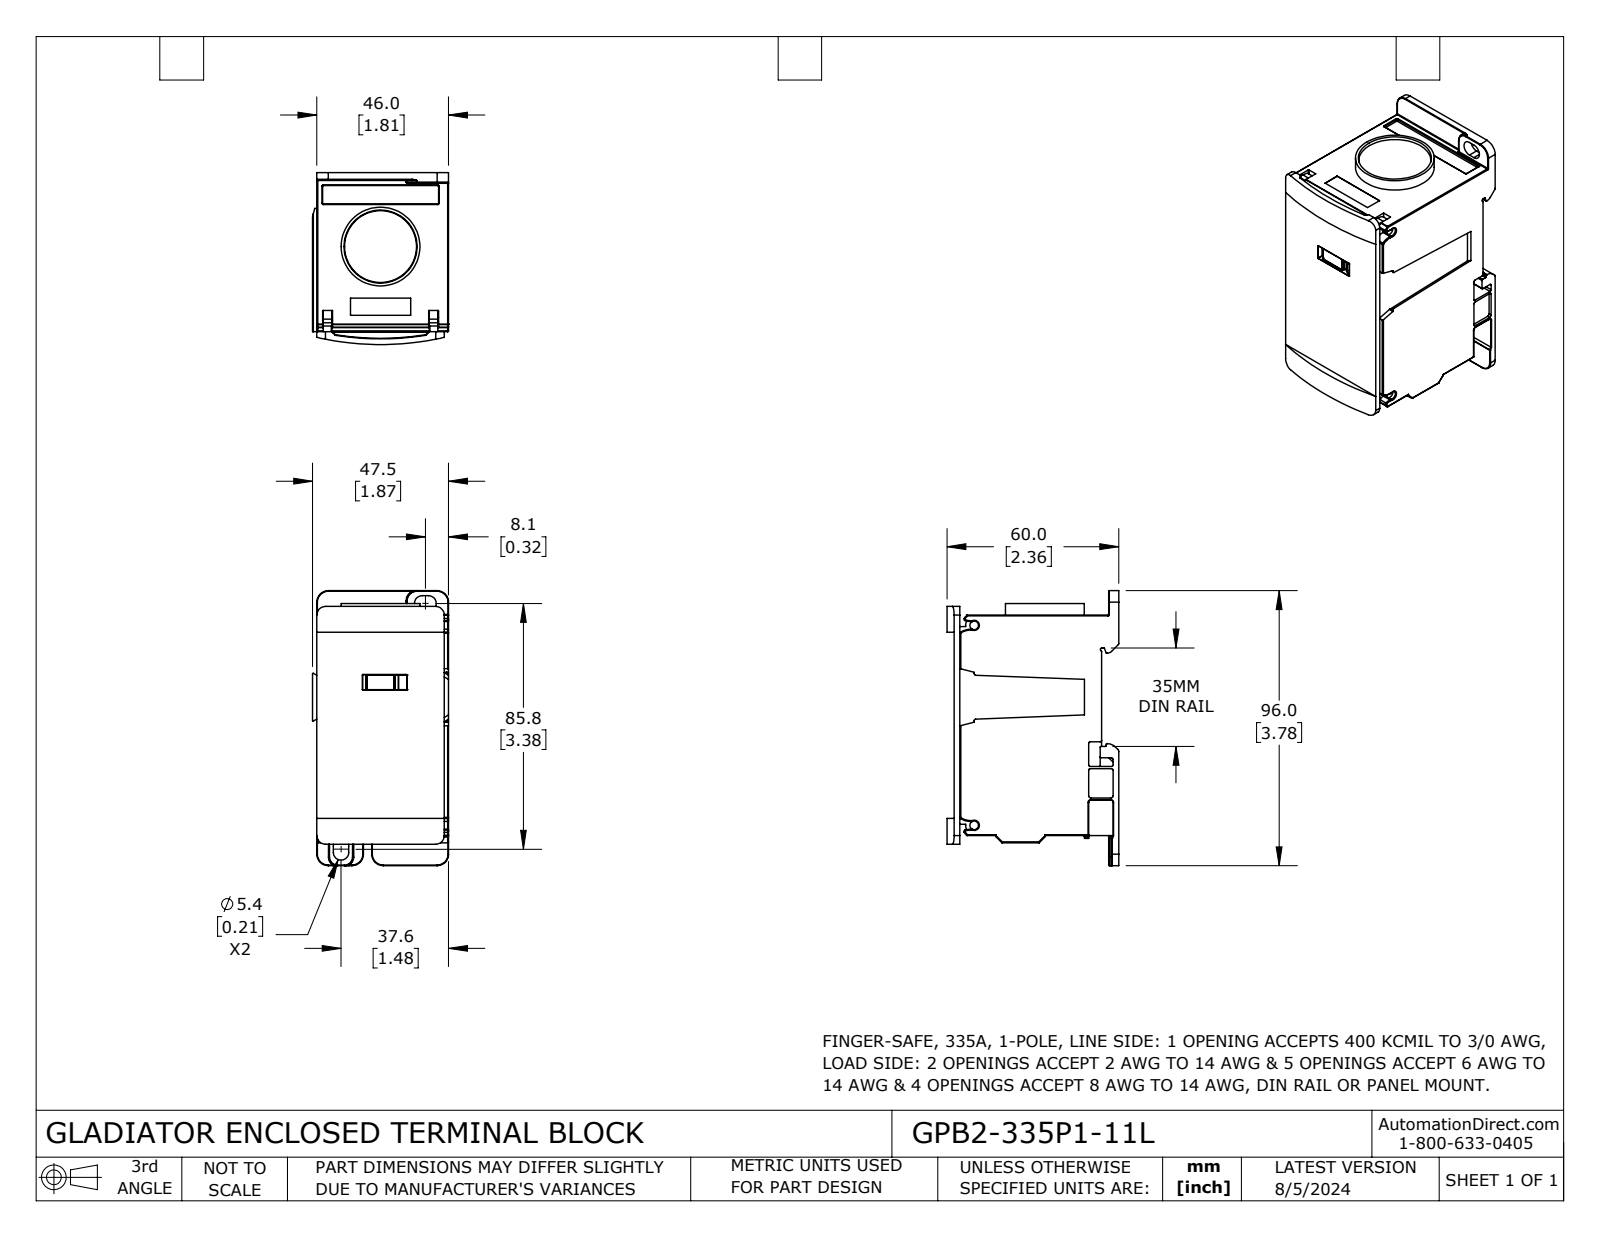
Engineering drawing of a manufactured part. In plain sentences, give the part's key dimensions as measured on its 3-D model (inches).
The part is named "GPB2-335P1-11L". Its 3-D file was written by "SolidWorks 2023 (CONFIG_CONTROL_DESIGN)". It is 1 solid with 651 faces: 219 planar, 299 cylindrical and 133 other. Overall it measures 3.787 by 2.362 by 1.87 inches. Its volume is 11.38 cubic inches and its surface area 49.55 square inches. Round holes: 5 of diameter 0.394, 4 of diameter 0.335, 2 of diameter 0.118, 2 of diameter 0.472. Round bosses or shafts: 1 of diameter 1.083. Partial cylindrical surfaces (rounded edges, fillets, slot ends): 85 of radius 0.008, 25 of radius 0.004, 24 of radius 0.012, 16 of radius 0.02, 9 of radius 0.157, 8 of radius 0.118, 6 of radius 0.03, 4 of radius 0.106. The main face-to-face distances are 1.811, 2.264, 0.079, 0.236, 0.039, 0.315, 0.098, 1.949, 2.028, 0.429. The hole center spacings are 0.374, 0.413, 0.557, 0.846, 0.926, 0.433, 0.454, 0.483.
